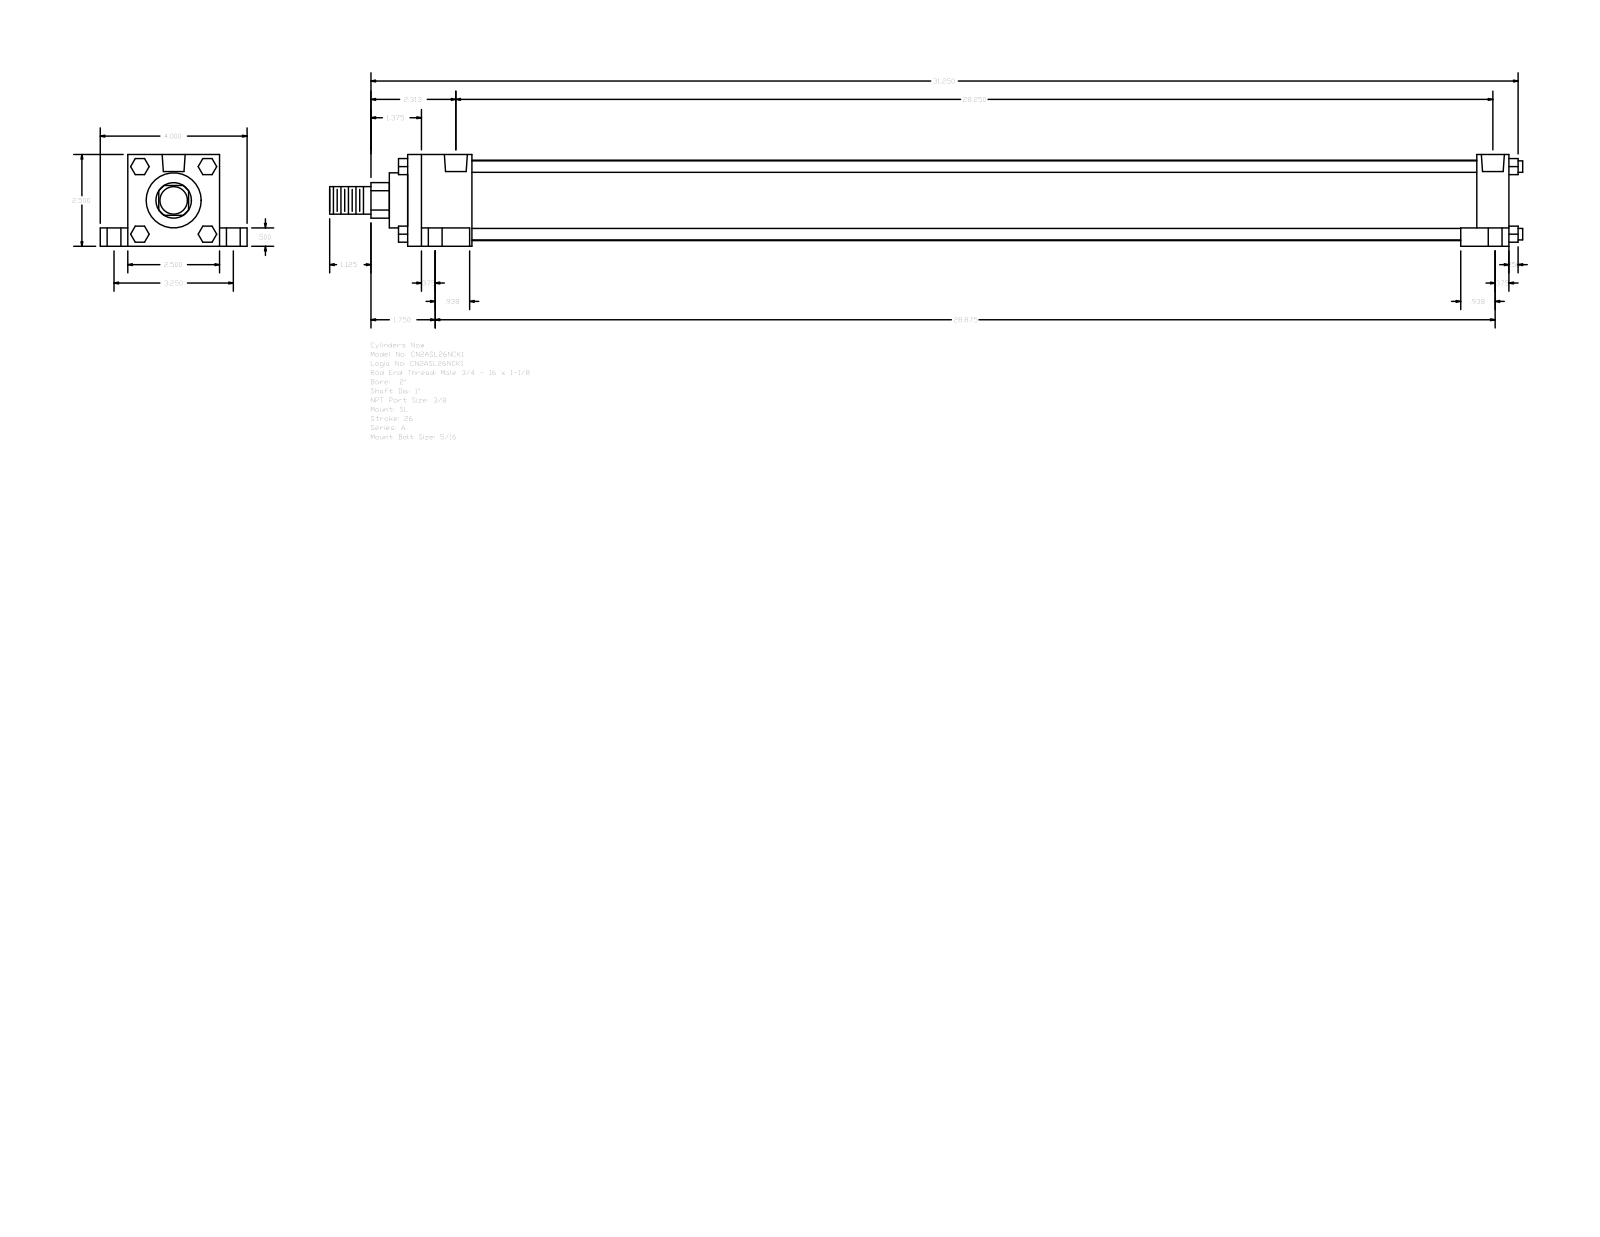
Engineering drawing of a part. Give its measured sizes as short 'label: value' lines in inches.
name: A_SL__0200_1
written by: GSSL Pune (CONFIG_CONTROL_DESIGN)
unit: in
bodies: 0 solids, 148 faces (112 planar, 36 cylindrical, 0 other)
size: 32.5 × 4 × 2.5
holes: 4× ⌀0.219, 4× ⌀0.375, 4× ⌀0.625, 2× ⌀0.627
bosses: 4× ⌀0.313, 1× ⌀2.19, 1× ⌀1.5, 1× ⌀1, 1× ⌀0.75
rounds: 1× R0.484
face distances: 2.5, 30, 0.5, 2, 0.75, 3.25, 1.75, 28.25, 29.125, 27.375
hole spacings: 1.626, 1.639, 1.719, 1.741, 3.25, 28.031, 28.297, 28.359
